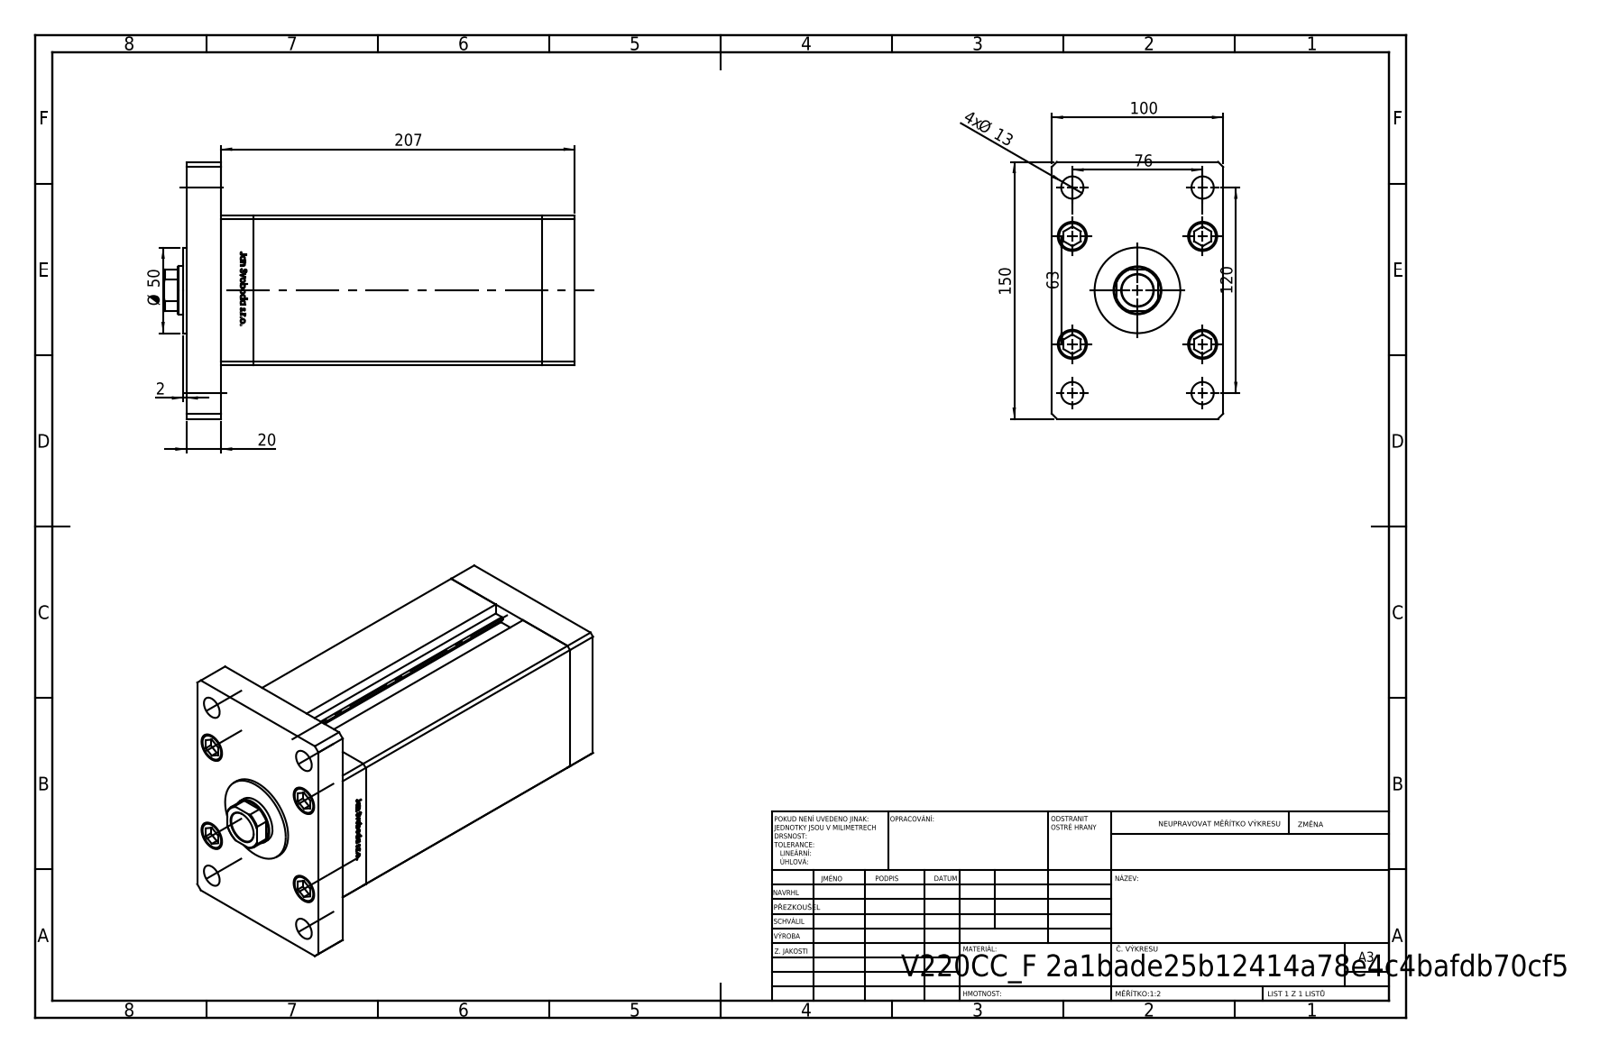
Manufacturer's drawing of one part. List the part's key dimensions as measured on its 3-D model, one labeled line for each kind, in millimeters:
Part name (STEP PRODUCT): ALLEN BOLT; V220C BACK_F; V220C_VC_F; V220C_F_MIDDLE (+2 more)
STEP written by: SolidWorks 2019 (CONFIG_CONTROL_DESIGN)
Units: millimetres
Bodies: 19 solids, 1311 faces (517 planar, 188 cylindrical, 606 other)
Overall size (bounding box): 239.5 × 150 × 100
Volume: 1 848 000 mm³ · Surface area: 272 154 mm²
Round holes (diameter × count): ⌀13.5 ×7, ⌀18 ×7, ⌀12 ×4, ⌀13 ×4, ⌀17 ×4, ⌀2 ×2, ⌀13.16 ×2, ⌀18.5 ×1, ⌀28 ×1, ⌀29.5 ×1
Round bosses / shafts (diameter × count): ⌀8 ×9, ⌀17 ×5, ⌀50 ×1
Partial cylindrical surfaces — rounded edges, fillets, slot ends (radius × count): R0.93 ×2, R13.5 ×1
Main face-to-face distances: 100, 19, 187.5, 87, 20, 168.5, 207.5, 39, 206.5, 226.5
Hole centre spacings: 34, 18.59, 28.5, 37.13, 39.64, 49.36, 57.95, 71.02
